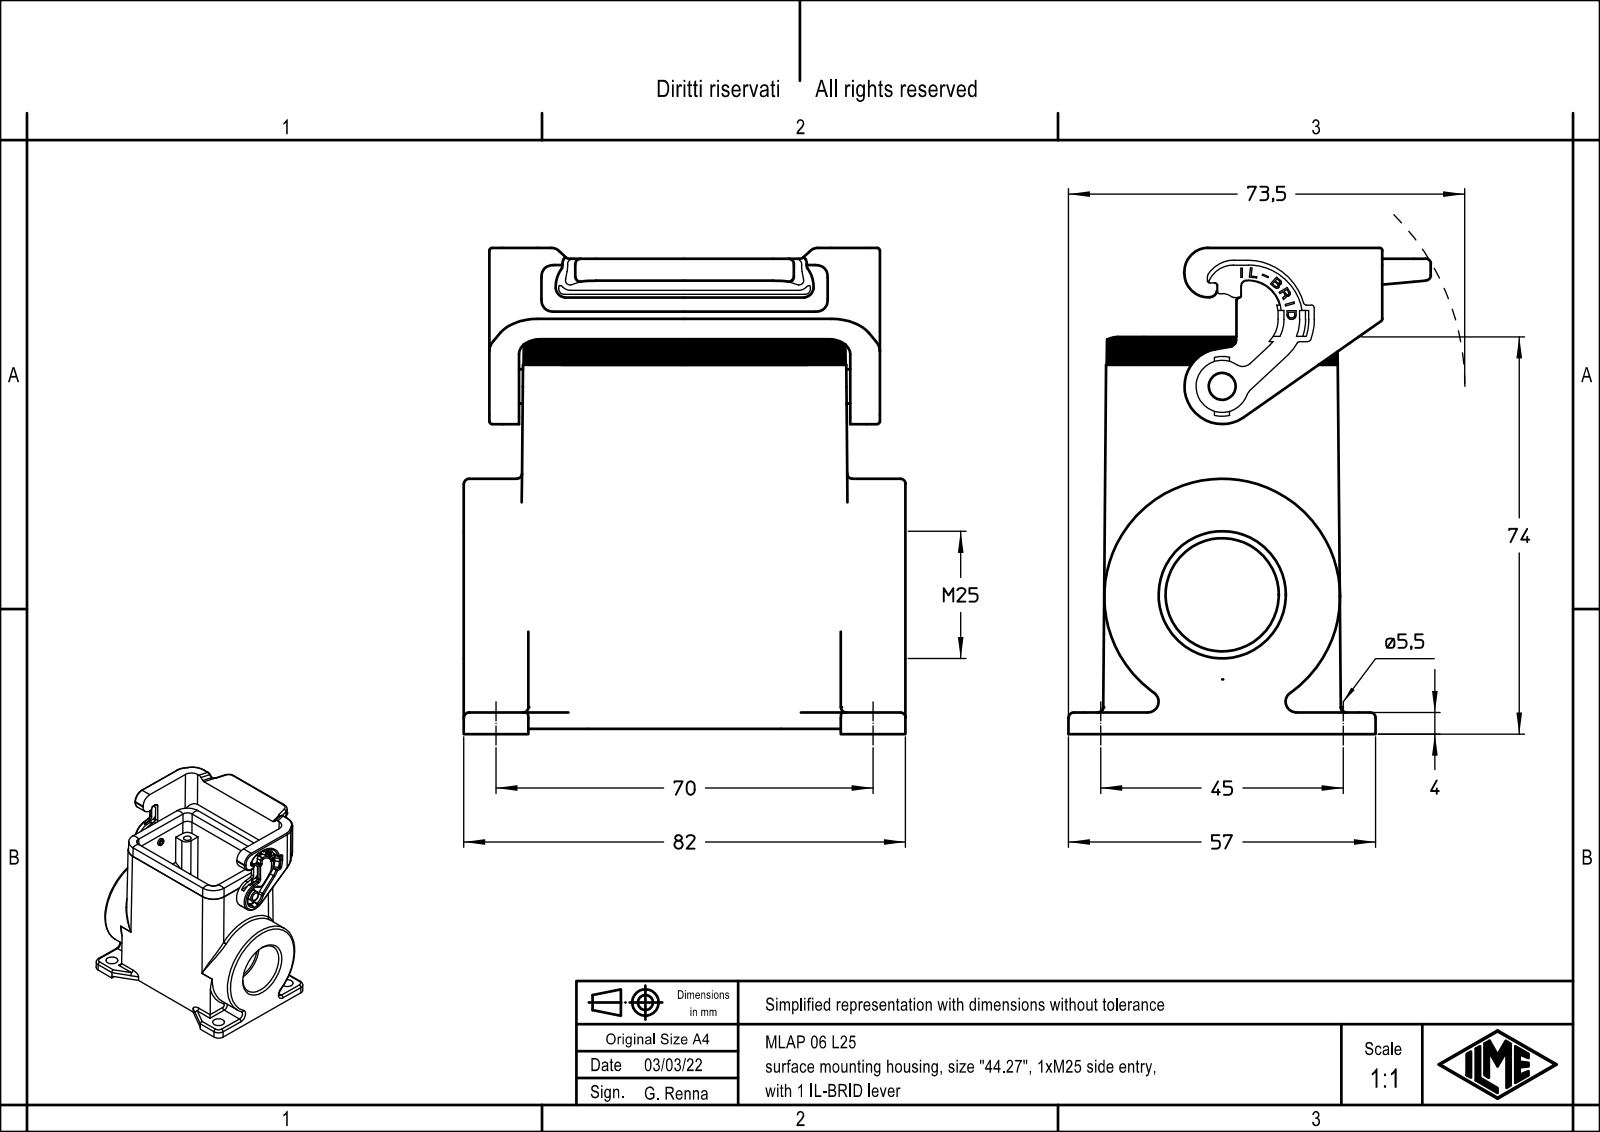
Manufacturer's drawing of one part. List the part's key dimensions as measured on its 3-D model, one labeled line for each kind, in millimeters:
Part name (STEP PRODUCT): MLAP_06_L25
STEP written by: Creo Elements/Direct Modeling 20.1B 02-Apr-2019 (C) Parametric Technology GmbH (AUTOMOTIVE_DESIGN)
Units: millimetres
Bodies: 1 solid, 706 faces (449 planar, 189 cylindrical, 68 other)
Overall size (bounding box): 90.2 × 82 × 67.25
Volume: 103 382 mm³ · Surface area: 46 915 mm²
Round holes (diameter × count): ⌀3.5 ×4, ⌀5.9 ×4, ⌀23.6 ×1, ⌀32 ×1, ⌀35.7 ×1
Round bosses / shafts (diameter × count): ⌀43 ×1, ⌀6.4 ×1, ⌀4.8 ×1
Partial cylindrical surfaces — rounded edges, fillets, slot ends (radius × count): R1 ×31, R3 ×16, R1.5 ×10, R2 ×10, R7 ×6, R0.3 ×4, R3.1 ×4, R4 ×4
Main face-to-face distances: 3.75, 39.25, 43, 35.5, 10.25, 4, 7, 3.65, 60.25, 61.5
Hole centre spacings: 15.81, 38.28, 57.71, 67.42, 27, 44, 45, 51.62
